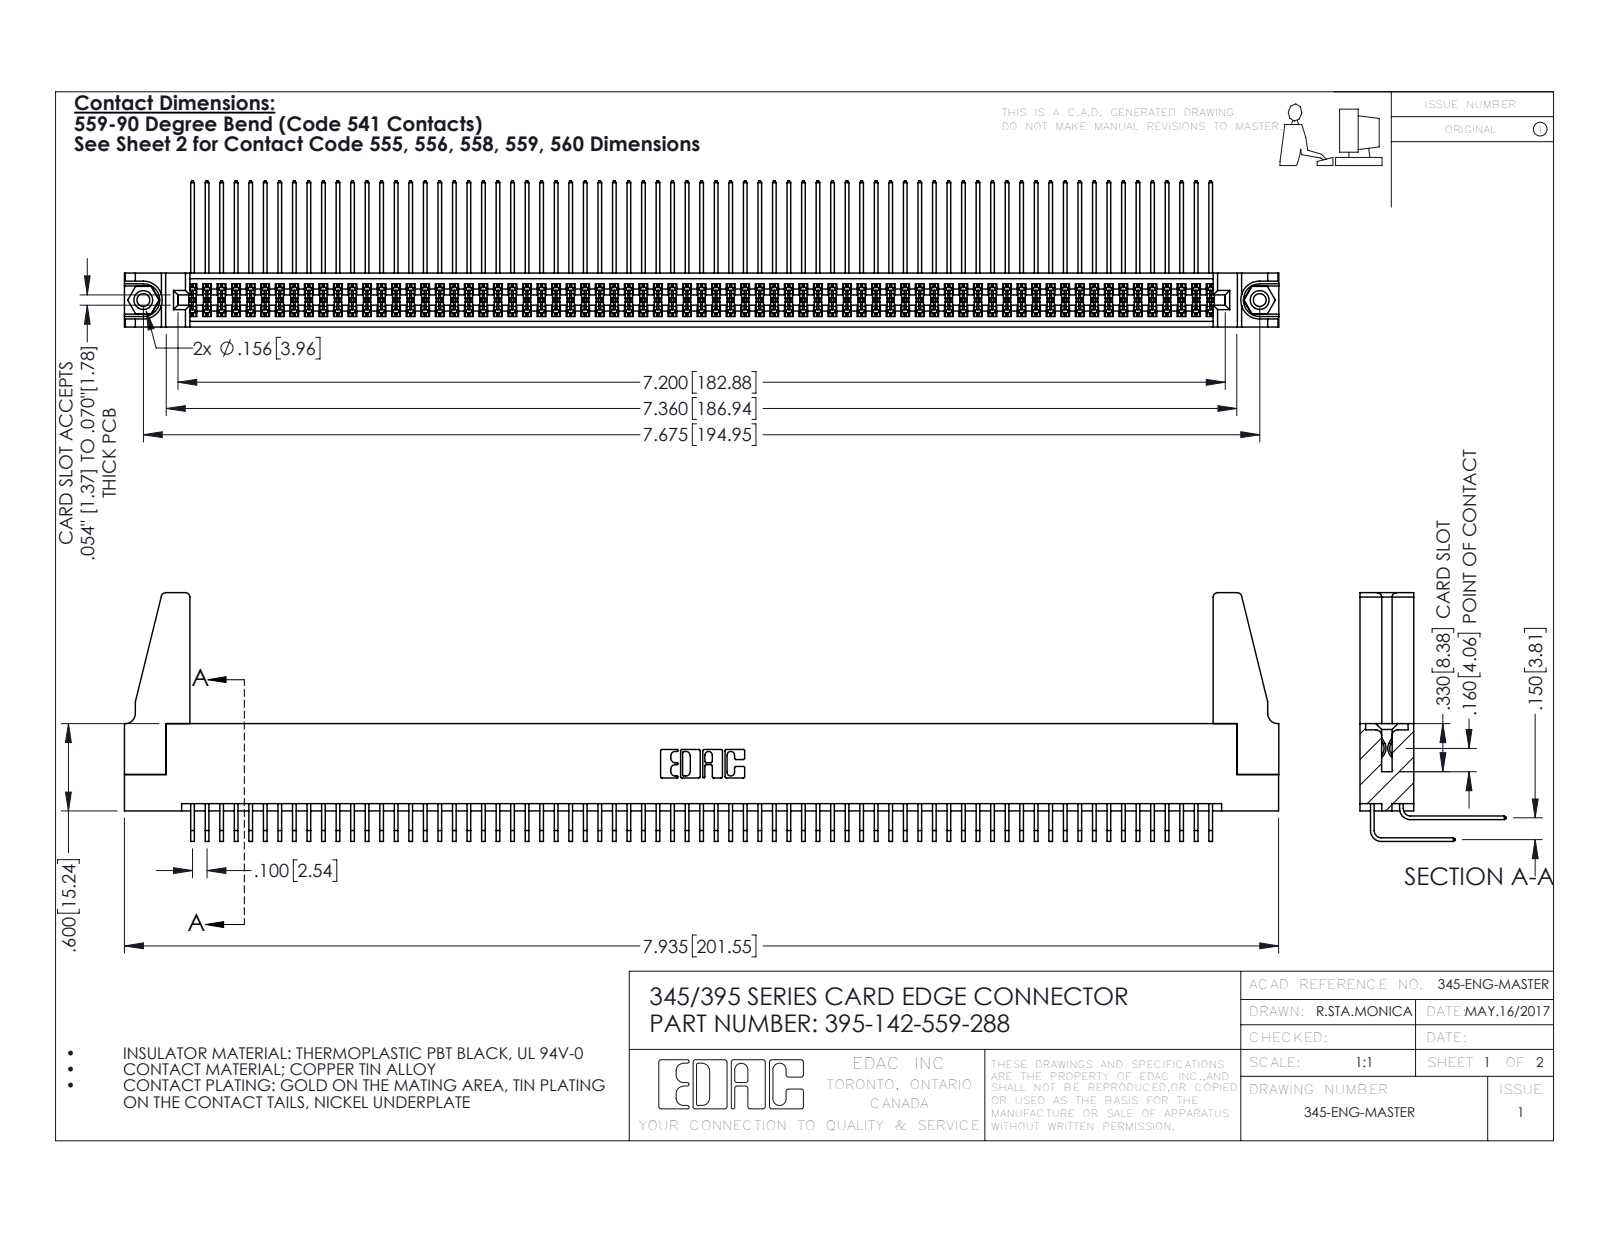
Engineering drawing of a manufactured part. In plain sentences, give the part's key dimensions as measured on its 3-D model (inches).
The part is named "345-220-078_345-220-088; 345-250-001_345-250-001-102; 345-292-001_559 Tail - 2; 395-142-559-288 (+2 more)". Its 3-D file was written by "SolidWorks 2016 (CONFIG_CONTROL_DESIGN)". It is 147 solids with 7634 faces: 5122 planar, 2496 cylindrical and 16 other. Overall it measures 7.936 by 1.709 by 1.005 inches. Its volume is 1.46 cubic inches and its surface area 59.04 square inches. Round holes: 2 of diameter 0.089, 2 of diameter 0.125, 2 of diameter 0.156, 1 of diameter 0.064. Round bosses or shafts: 2 of diameter 0.155. Partial cylindrical surfaces (rounded edges, fillets, slot ends): 284 of radius 0.006, 22 of radius 0.01, 8 of radius 0.03, 6 of radius 0.007, 6 of radius 0.031, 3 of radius 0.026, 2 of radius 0.014, 2 of radius 0.019. The main face-to-face distances are 0.072, 0.298, 0.37, 0.2, 0.098, 0.272, 0.025, 0.225, 0.175, 0.15. The hole center spacings are 0.27, 7.439, 7.675.
